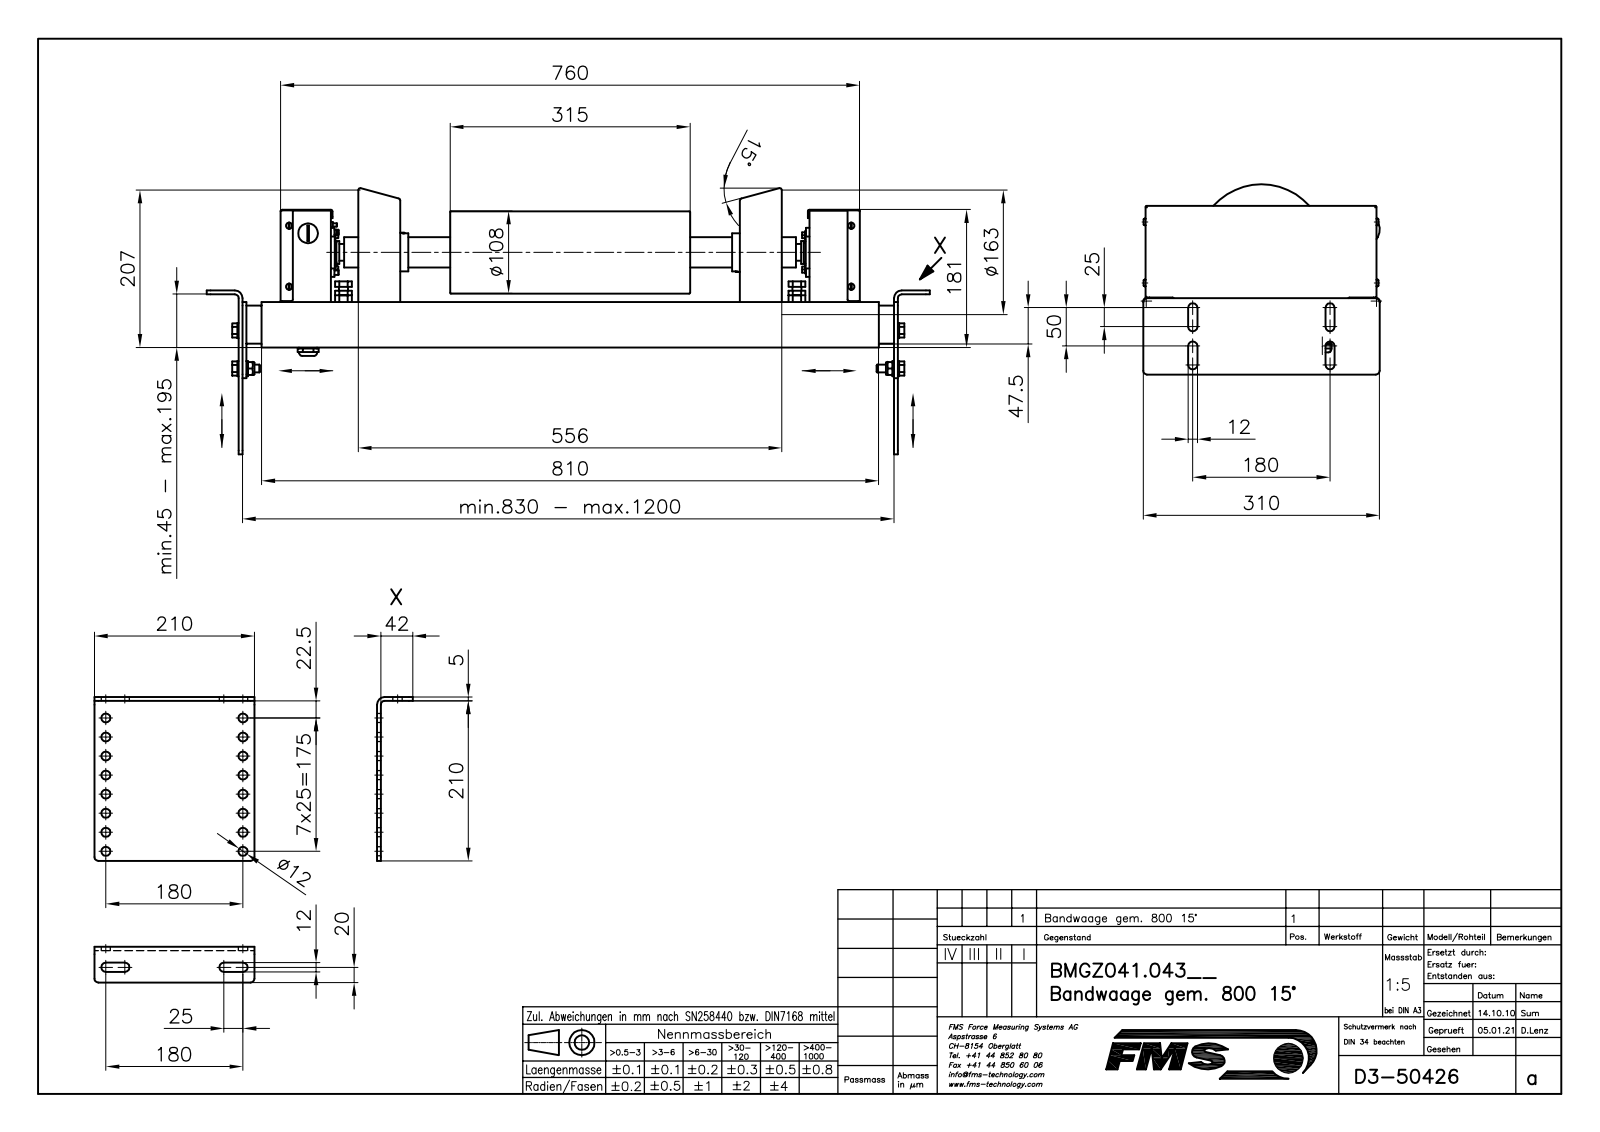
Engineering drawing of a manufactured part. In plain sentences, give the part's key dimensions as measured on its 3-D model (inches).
The part is named "B50426_STP; B50030; 6KT-SCHRAUBE_M12X30; ZYL_SCHR__M4X8 (+8 more)". Its 3-D file was written by "Mechanical Desktop 2009 (CONFIG_CONTROL_DESIGN)". It is 156 solids with 2602 faces: 1343 planar, 932 cylindrical and 327 other. Overall it measures 37.362 by 13.75 by 12.213 inches. Its volume is 533.1 cubic inches and its surface area 3 957 square inches. Round holes: 17 of diameter 0.472, 6 of diameter 0.197, 4 of diameter 0.138, 4 of diameter 0.193, 4 of diameter 0.252, 4 of diameter 0.342, 4 of diameter 0.344, 4 of diameter 0.394, 4 of diameter 0.413, 4 of diameter 0.42, 4 of diameter 0.583, 3 of diameter 0.236. Round bosses or shafts: 11 of diameter 0.472, 8 of diameter 0.323, 8 of diameter 0.165, 6 of diameter 0.787, 6 of diameter 0.394, 5 of diameter 0.197, 4 of diameter 0.63, 4 of diameter 0.437. Partial cylindrical surfaces (rounded edges, fillets, slot ends): 34 of radius 0.079, 24 of radius 0.039, 16 of radius 0.157, 16 of radius 0.197, 14 of radius 0.236, 8 of radius 0.138, 6 of radius 0.089, 4 of radius 0.02. The main face-to-face distances are 0.157, 0.197, 0.039, 2.008, 1.417, 10.63, 1.811, 1.969, 0.118, 2.205. The hole center spacings are 0.984, 7.155, 1.969, 7.355, 2.953, 7.677, 3.937, 7.087.
